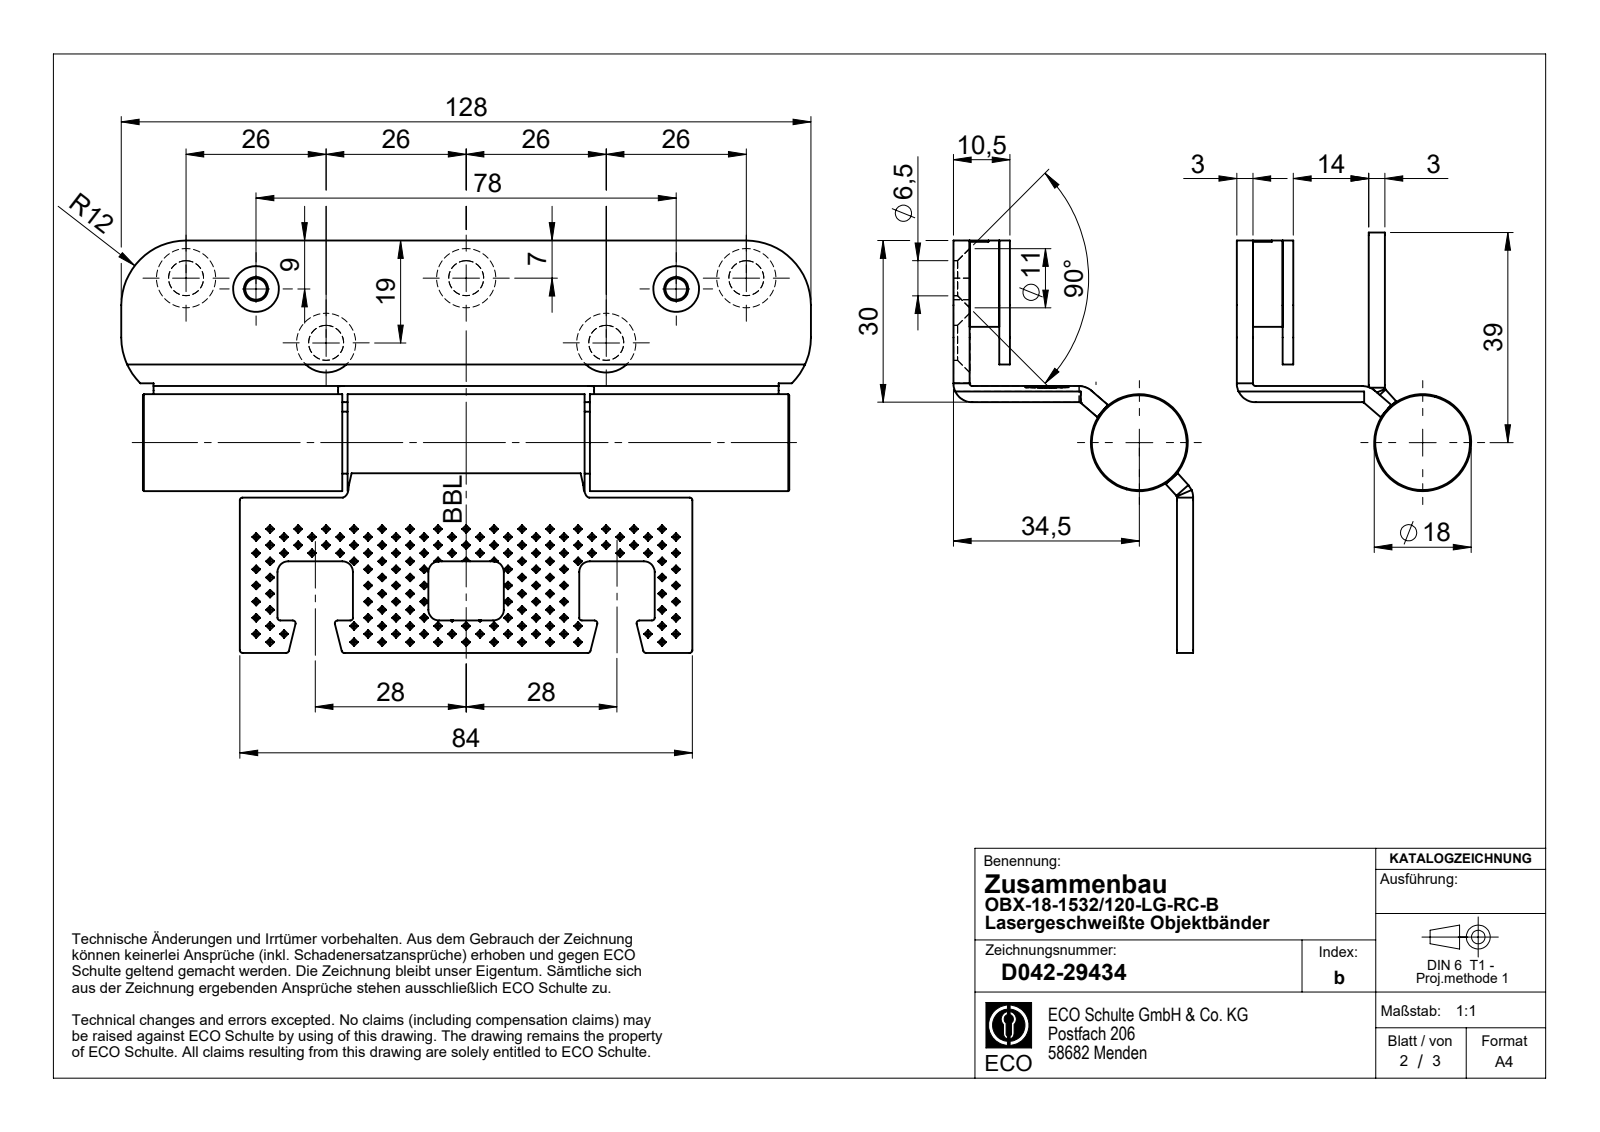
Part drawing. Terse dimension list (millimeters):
name: D044-24252; D044-14308; DIN5401-III; D043-24287 (+6 more)
written by: SolidWorks 2020 (CONFIG_CONTROL_DESIGN)
unit: mm
bodies: 13 solids, 1821 faces (1558 planar, 158 cylindrical, 105 other)
size: 128 × 48 × 43.5
volume: 65 181 mm³; area: 46 197 mm²
holes: 5× ⌀6.5, 2× ⌀2, 2× ⌀4, 2× ⌀5, 1× ⌀0.5, 1× ⌀4.5, 1× ⌀7.9
bosses: 1× ⌀18, 1× ⌀12, 1× ⌀11.8, 1× ⌀11.5, 1× ⌀7.7, 1× ⌀4, 1× ⌀1.65
rounds: 19× R0.5, 8× R2, 6× R0.25, 4× R12, 3× R3.5, 2× R0.68, 2× R1, 2× R2.1
face distances: 3, 2, 24.5, 5.5, 8.5, 14, 7.5, 16, 10.5, 4
hole spacings: 28.64, 52, 13.15, 16.4, 39.05, 65.76, 78.92, 91.02
